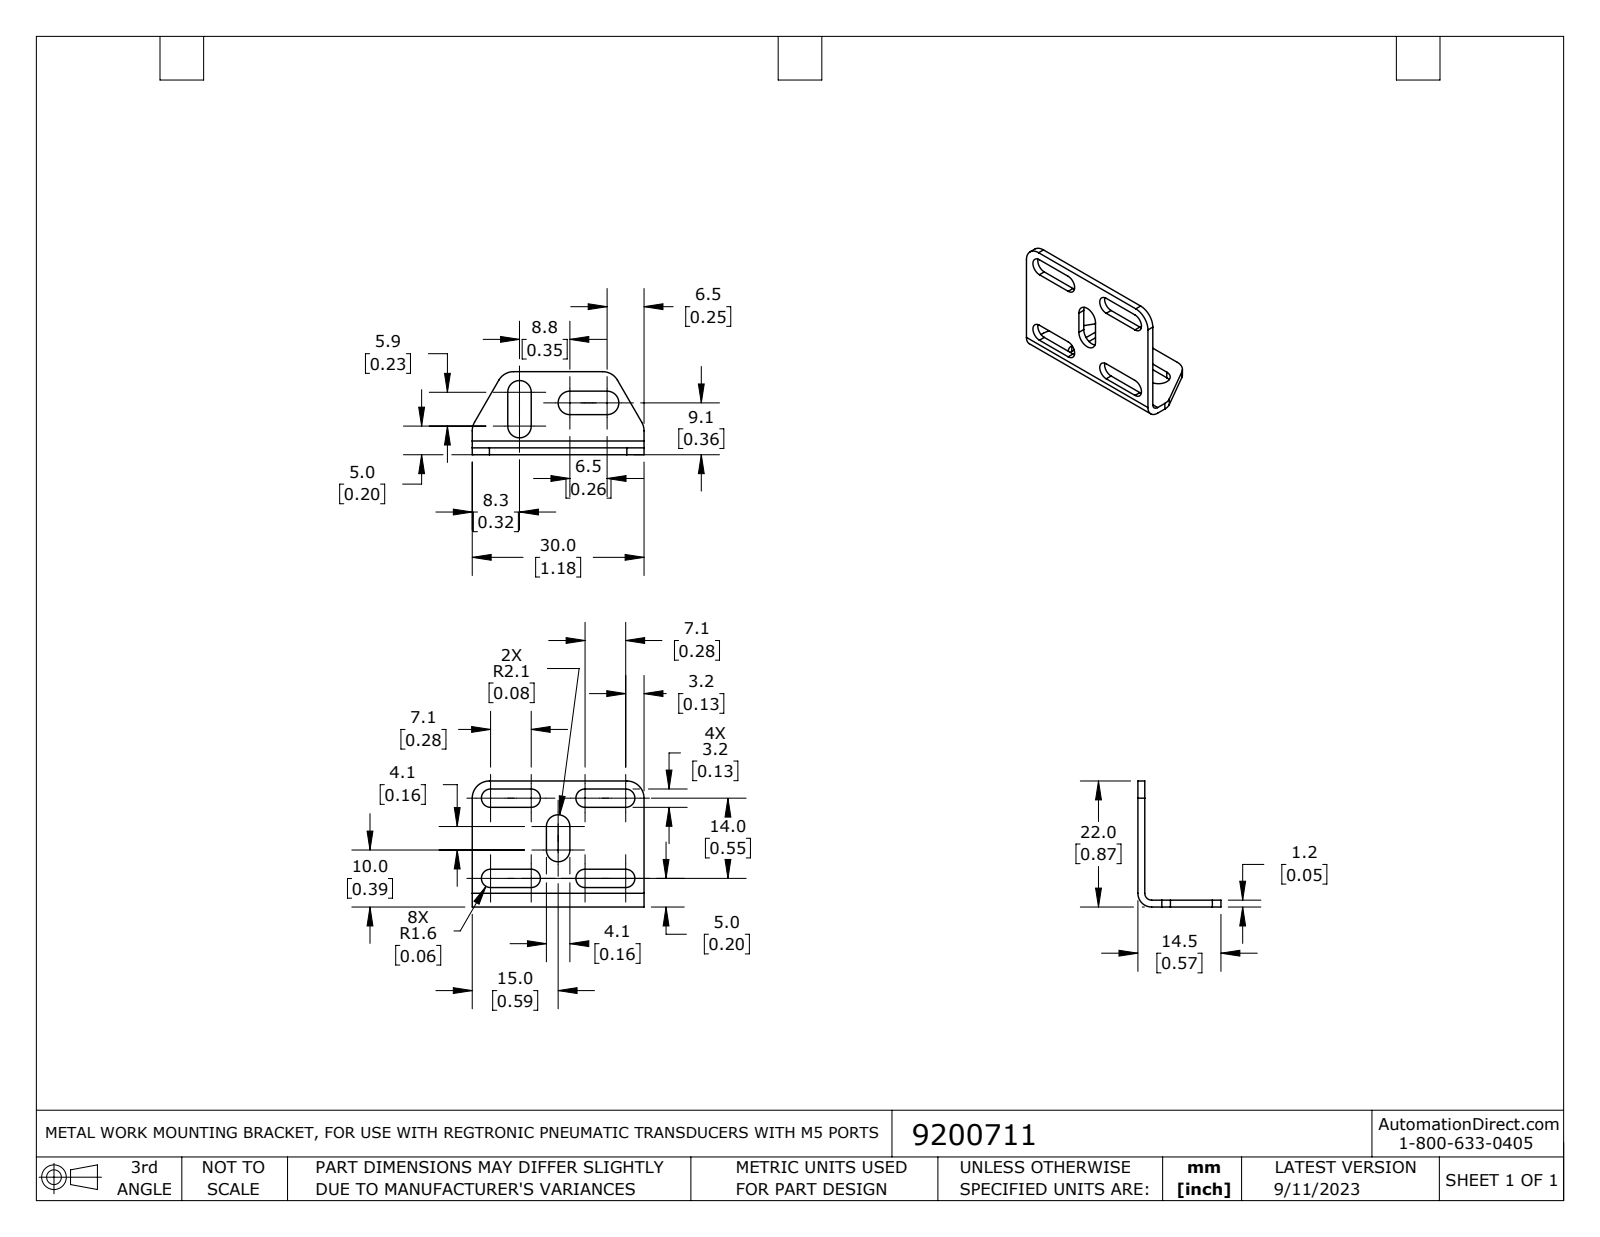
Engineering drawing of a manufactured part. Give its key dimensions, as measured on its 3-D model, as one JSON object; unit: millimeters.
{"part_name": "9200711", "step_written_by": "SolidWorks 2021 (AUTOMOTIVE_DESIGN)", "units": "millimeters", "bodies": {"solids": 1, "faces": 46, "planar": 24, "cylindrical": 22, "other": 0}, "overall_size": [30, 22, 14.5], "volume_mm3": 900, "surface_area_mm2": 1840, "partial_cylinders_radius": [[1.6, 8], [2.1, 6], [3, 6], [1.2, 1], [2.4, 1]], "face_to_face_distances": [1.2, 3.2, 14, 22, 20.8, 30, 3.4, 4.1, 13.3, 14.5]}
